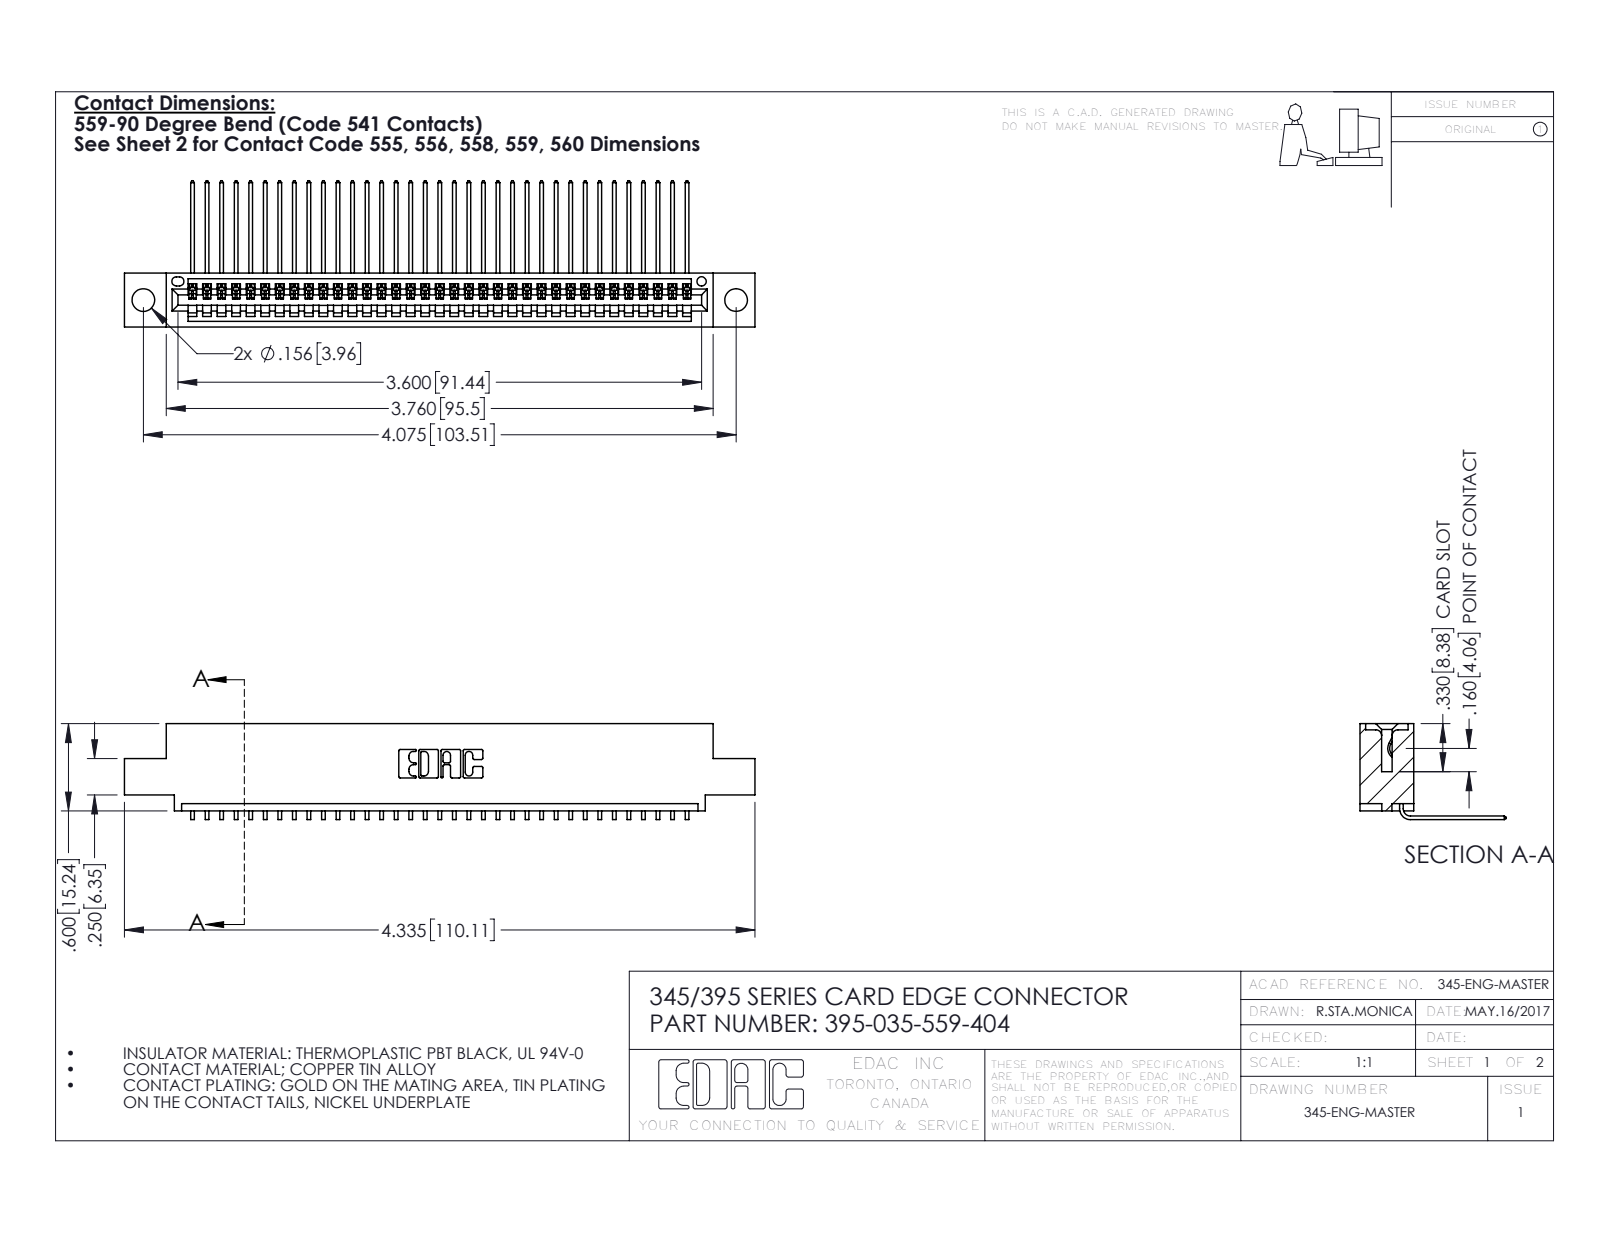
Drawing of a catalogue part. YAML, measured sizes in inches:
part_name: "345 Part_0.110 Offset - 0.156 Dia-TH; 345-292-001_558 559 Tail - 1; 395-035-559-404"
step_written_by: "SolidWorks 2016 (CONFIG_CONTROL_DESIGN)"
units: inches
bodies: {solids: 36, faces: 2230, planar: 1554, cylindrical: 676, other: 0}
overall_size: [4.335, 1.005, 0.659]
volume: 0.632
surface_area: 22.08
round_holes:
  - {diameter: 0.156, count: 2}
  - {diameter: 0.064, count: 1}
partial_cylinders:
  - {radius: 0.006, count: 70}
  - {radius: 0.01, count: 22}
  - {radius: 0.007, count: 6}
  - {radius: 0.031, count: 6}
  - {radius: 0.026, count: 3}
  - {radius: 0.031, count: 2}
  - {radius: 0.04, count: 2}
  - {radius: 0.014, count: 1}
face_to_face_distances: [0.072, 0.298, 0.37, 0.2, 0.098, 0.272, 0.025, 0.225, 0.149, 0.072]
hole_center_spacings: [0.27, 3.839, 4.075]
